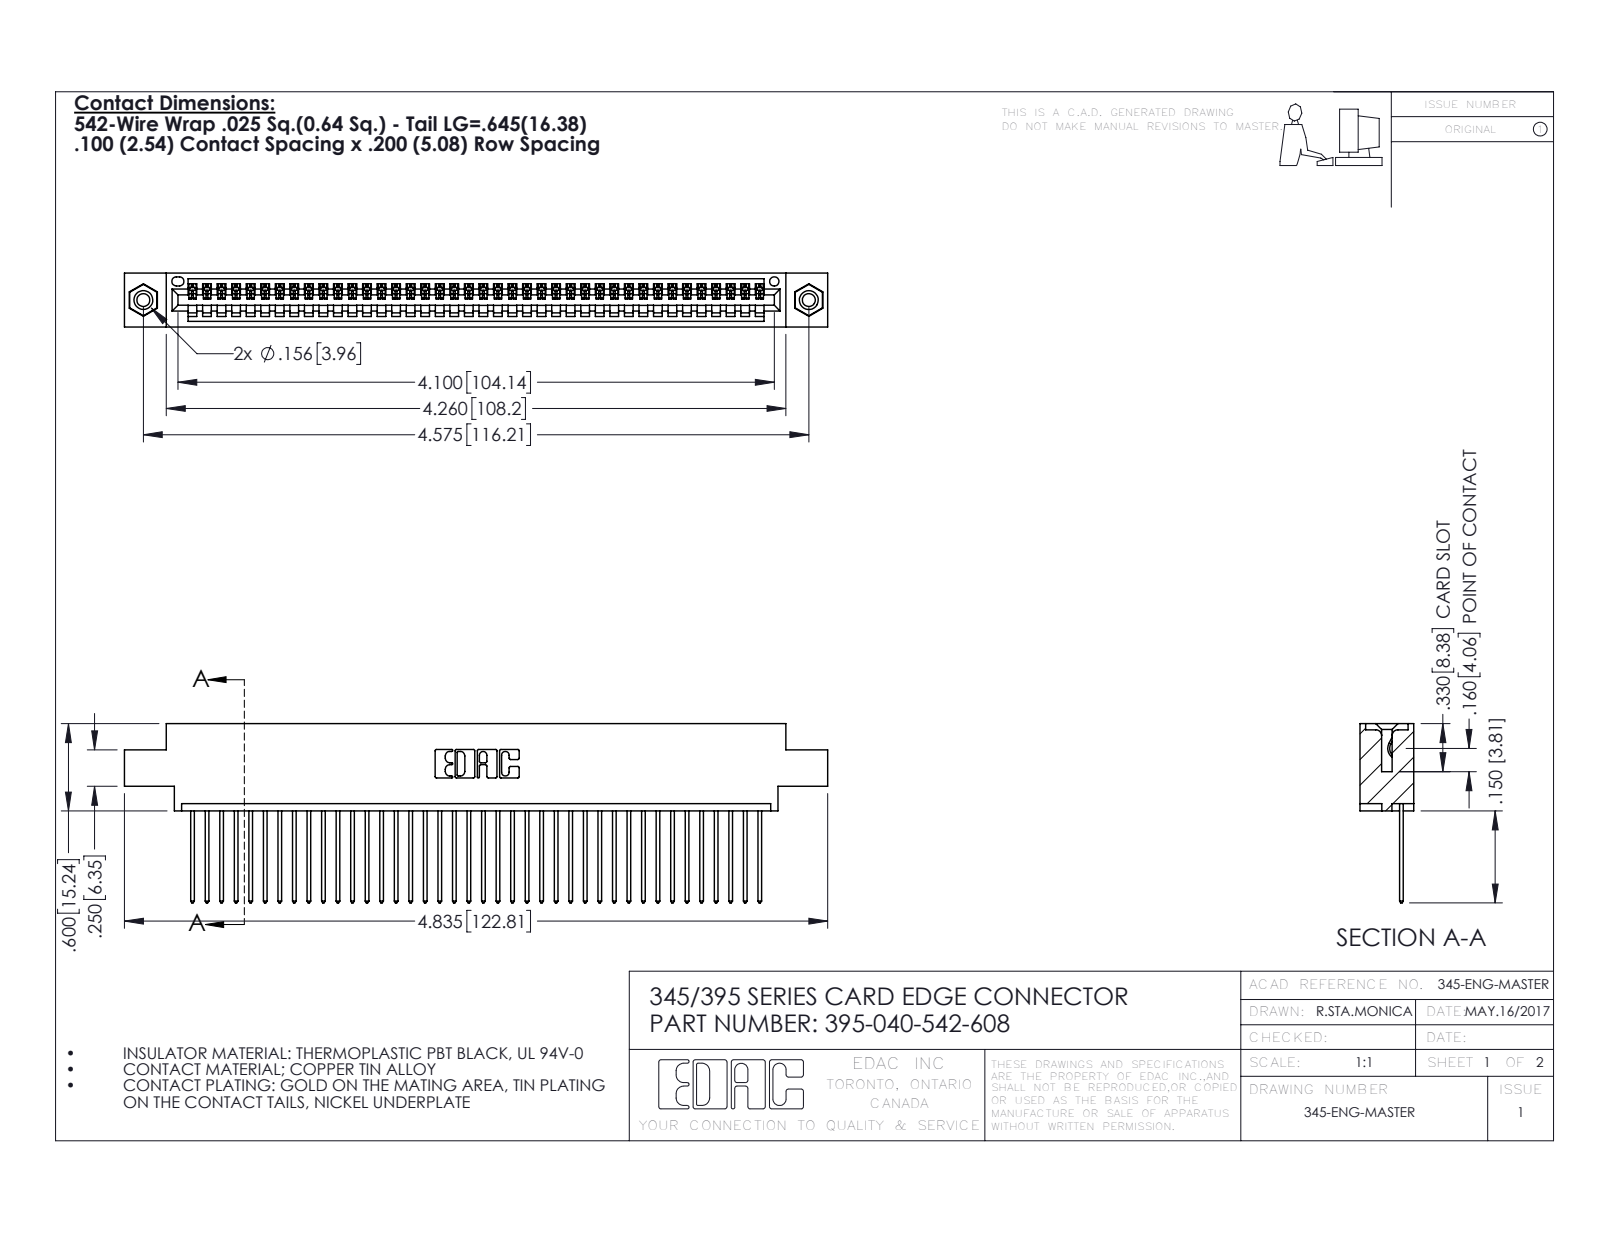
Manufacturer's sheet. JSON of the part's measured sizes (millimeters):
{"part_name": "345 Part_0.170 Offset - 0.156 Dia-TI; 395-040-542-608; 345-250-001_345-250-003-102; 345-292-001_345-293-142", "step_written_by": "SolidWorks 2016 (CONFIG_CONTROL_DESIGN)", "units": "millimeters", "bodies": {"solids": 43, "faces": 2510, "planar": 1716, "cylindrical": 778, "other": 16}, "overall_size": [122.8, 31.3, 9.4], "volume_mm3": 11600, "surface_area_mm2": 16120, "round_holes": [[2.3, 2], [3.2, 2], [4, 2], [1.6, 1]], "round_bosses_or_shafts": [[3.9, 2]], "partial_cylinders_radius": [[0.2, 80], [0.3, 80], [0.3, 22], [0.2, 6], [0.8, 6], [0.7, 3], [0.8, 2], [1, 2]], "face_to_face_distances": [1.8, 7.6, 9.4, 2.5, 6.9, 0.6, 5.1, 5.7, 4.4, 3.8], "hole_center_spacings": [6.9, 110.2, 116.2]}
